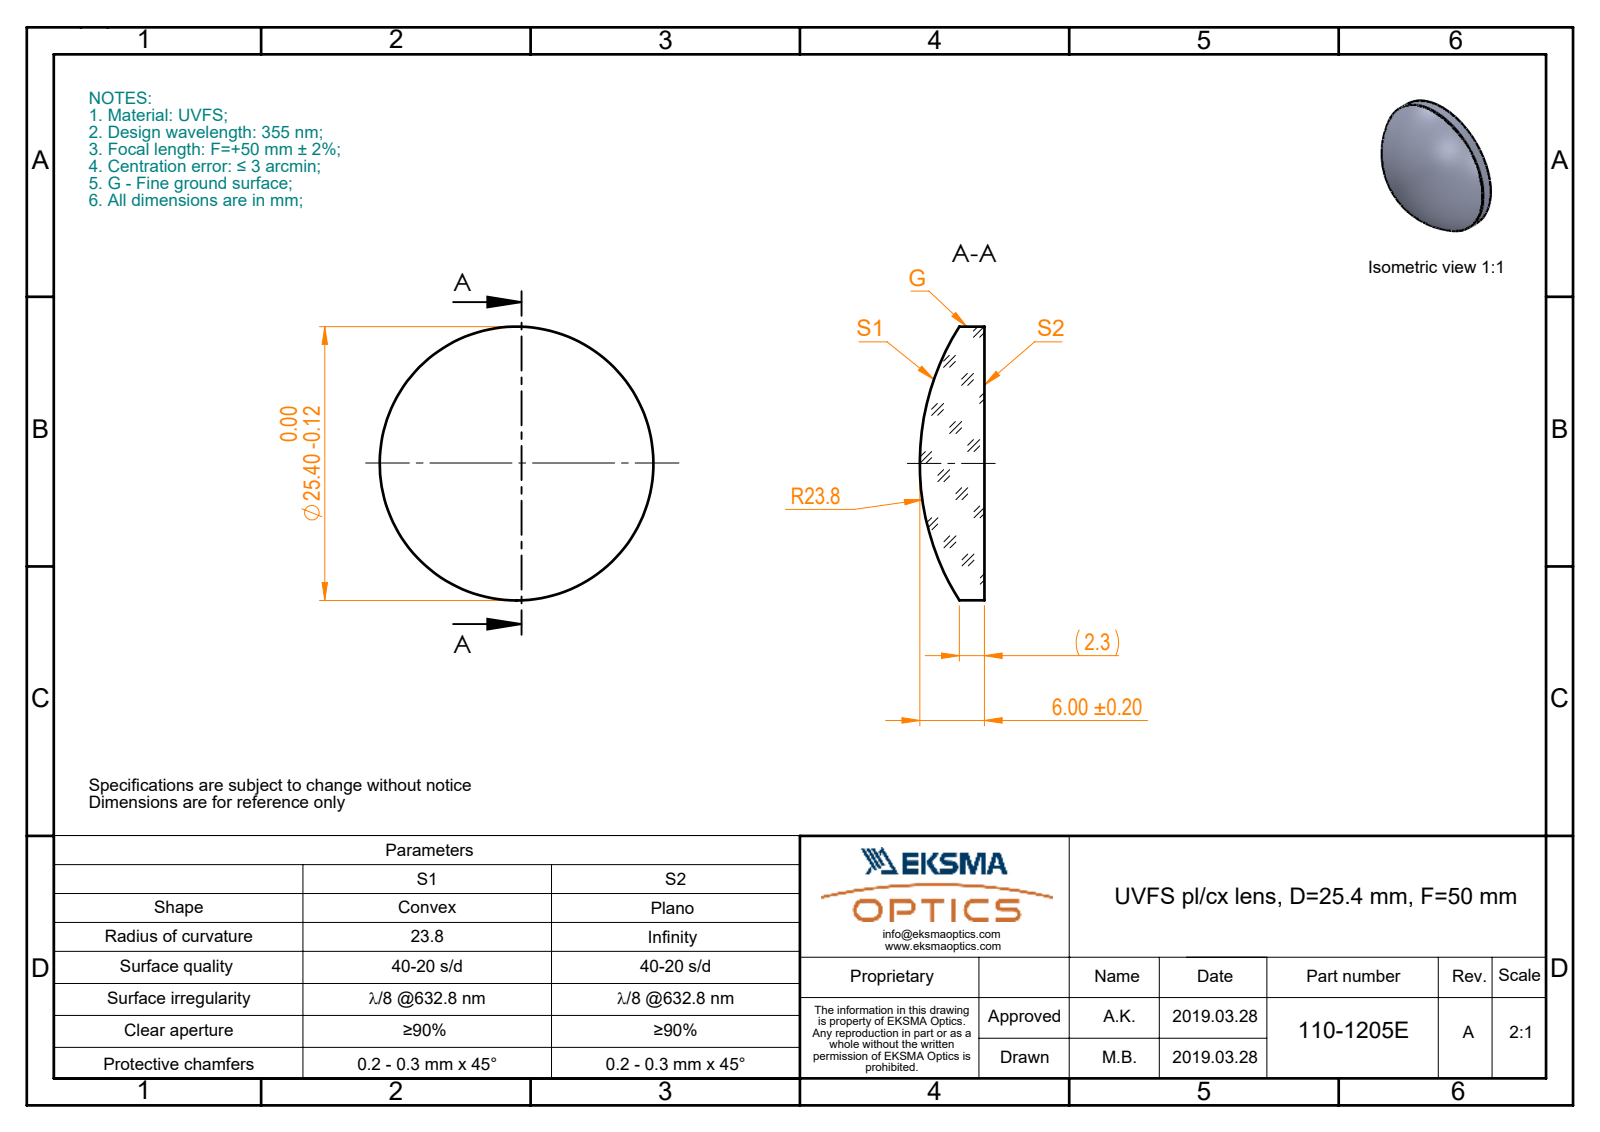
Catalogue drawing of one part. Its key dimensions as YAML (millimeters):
part_name: "110-1205E UVFS pl-cx 25.4 F50"
step_written_by: "SolidWorks 2017 (CONFIG_CONTROL_DESIGN)"
units: millimeters
bodies: {solids: 1, faces: 5, planar: 1, cylindrical: 2, other: 2}
overall_size: [25.4, 25.4, 6]
volume: 2136
surface_area: 1242
round_bosses_or_shafts:
  - {diameter: 25.4, count: 1}
